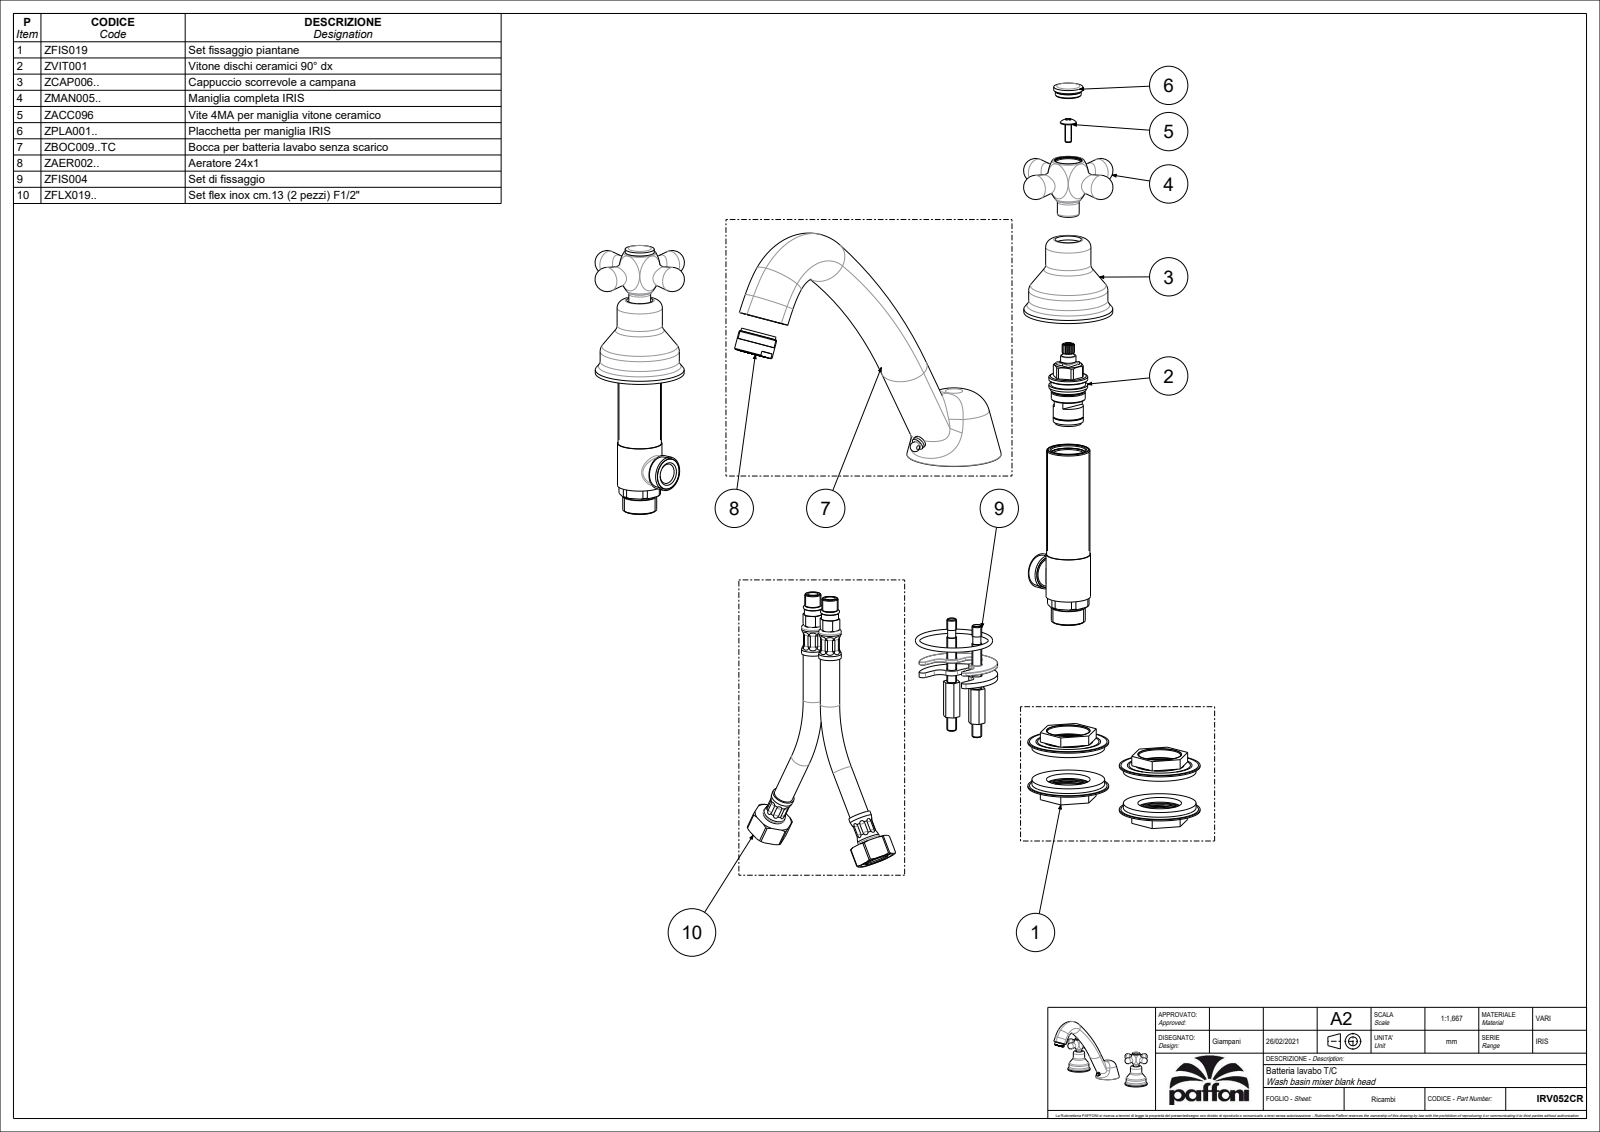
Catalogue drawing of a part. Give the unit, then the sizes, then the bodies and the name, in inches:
Units: inches
Overall size (bounding box): 10.709 × 8.547 × 6.513
Round holes (diameter × count): ⌀0.217 ×2, ⌀0.354 ×2, ⌀0.433 ×2, ⌀0.63 ×1, ⌀0.787 ×1, ⌀0.827 ×1, ⌀0.906 ×1, ⌀1.89 ×1
Round bosses / shafts (diameter × count): ⌀2.165 ×2, ⌀1.929 ×2, ⌀1.102 ×2, ⌀0.709 ×2, ⌀0.531 ×2, ⌀1.654 ×1, ⌀0.945 ×1, ⌀0.315 ×1
Partial cylindrical surfaces — rounded edges, fillets, slot ends (radius × count): R0.039 ×8, R0.098 ×8, R0.031 ×5, R0.197 ×2, R0.073 ×1, R0.736 ×1, R0.787 ×1
Main face-to-face distances: 0.354, 0.118, 0.079, 0.276, 0.305, 0.236, 0.303, 1.476, 1.831, 1.752
Hole centre spacings: 0.378, 0.559, 0.606, 0.938, 0.591, 0.866
Volume: 16.63 in³ · Surface area: 134.6 in²
Bodies: 3 solids, 370 faces (42 planar, 79 cylindrical, 249 other)
Part name (STEP PRODUCT): IRV052CR
STEP written by: CREO PARAMETRIC BY PTC INC, 2020044 (CONFIG_CONTROL_DESIGN)
